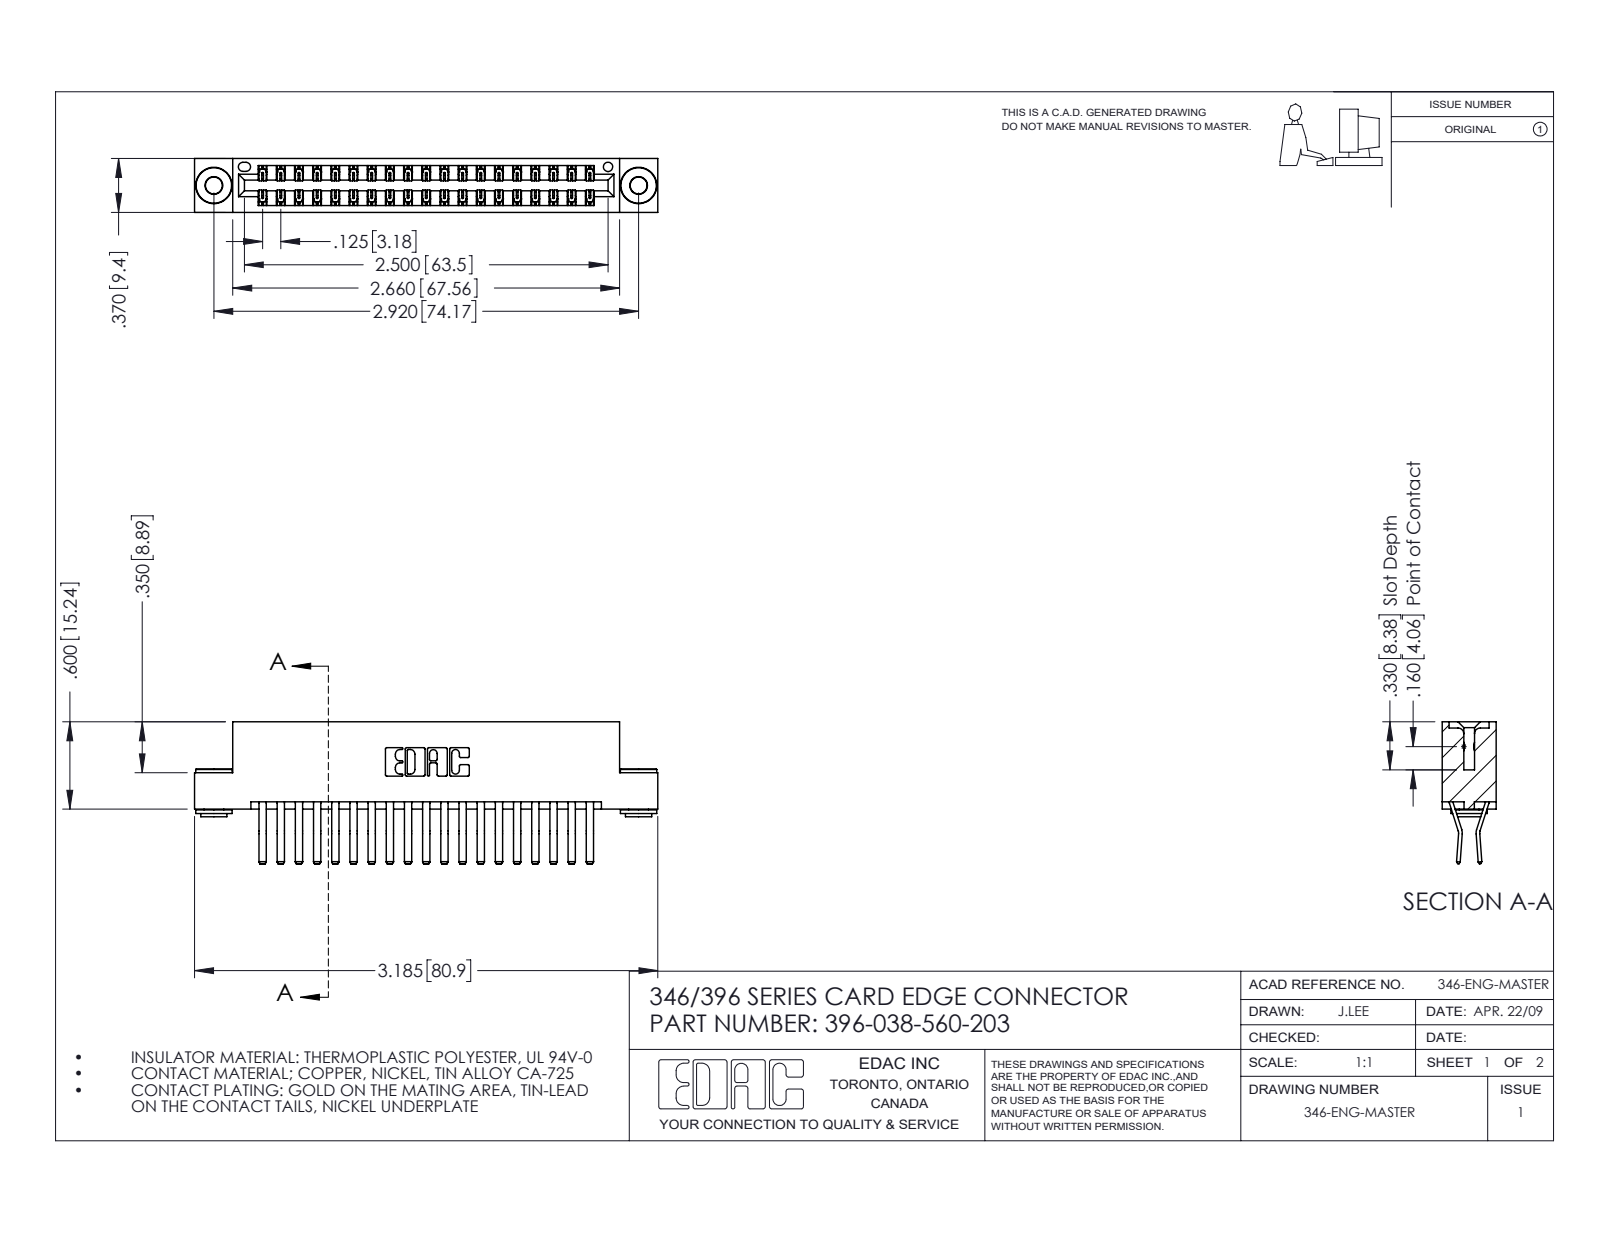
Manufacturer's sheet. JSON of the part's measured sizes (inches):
{"part_name": "346 Part_Flush Mounting Lugs - 0.156 Dia-TH; 345-250-002_345-250-002-102; 396-038-560-203; 345-292-001_560 Tail", "step_written_by": "SolidWorks 2016 (CONFIG_CONTROL_DESIGN)", "units": "inches", "bodies": {"solids": 41, "faces": 2212, "planar": 1416, "cylindrical": 788, "other": 8}, "overall_size": [3.185, 0.975, 0.37], "volume_in3": 0.487, "surface_area_in2": 17.8, "round_holes": [[0.116, 2], [0.156, 2], [0.064, 1]], "round_bosses_or_shafts": [[0.25, 2], [0.18, 2], [0.136, 2]], "partial_cylinders_radius": [[0.006, 57], [0.01, 22], [0.007, 6], [0.031, 6], [0.026, 3], [0.01, 2], [0.014, 2], [0.022, 2]], "face_to_face_distances": [0.048, 0.322, 0.25, 0.37, 0.025, 0.072, 0.298, 0.275, 0.148, 0.222], "hole_center_spacings": [0.246, 2.713, 2.92]}
